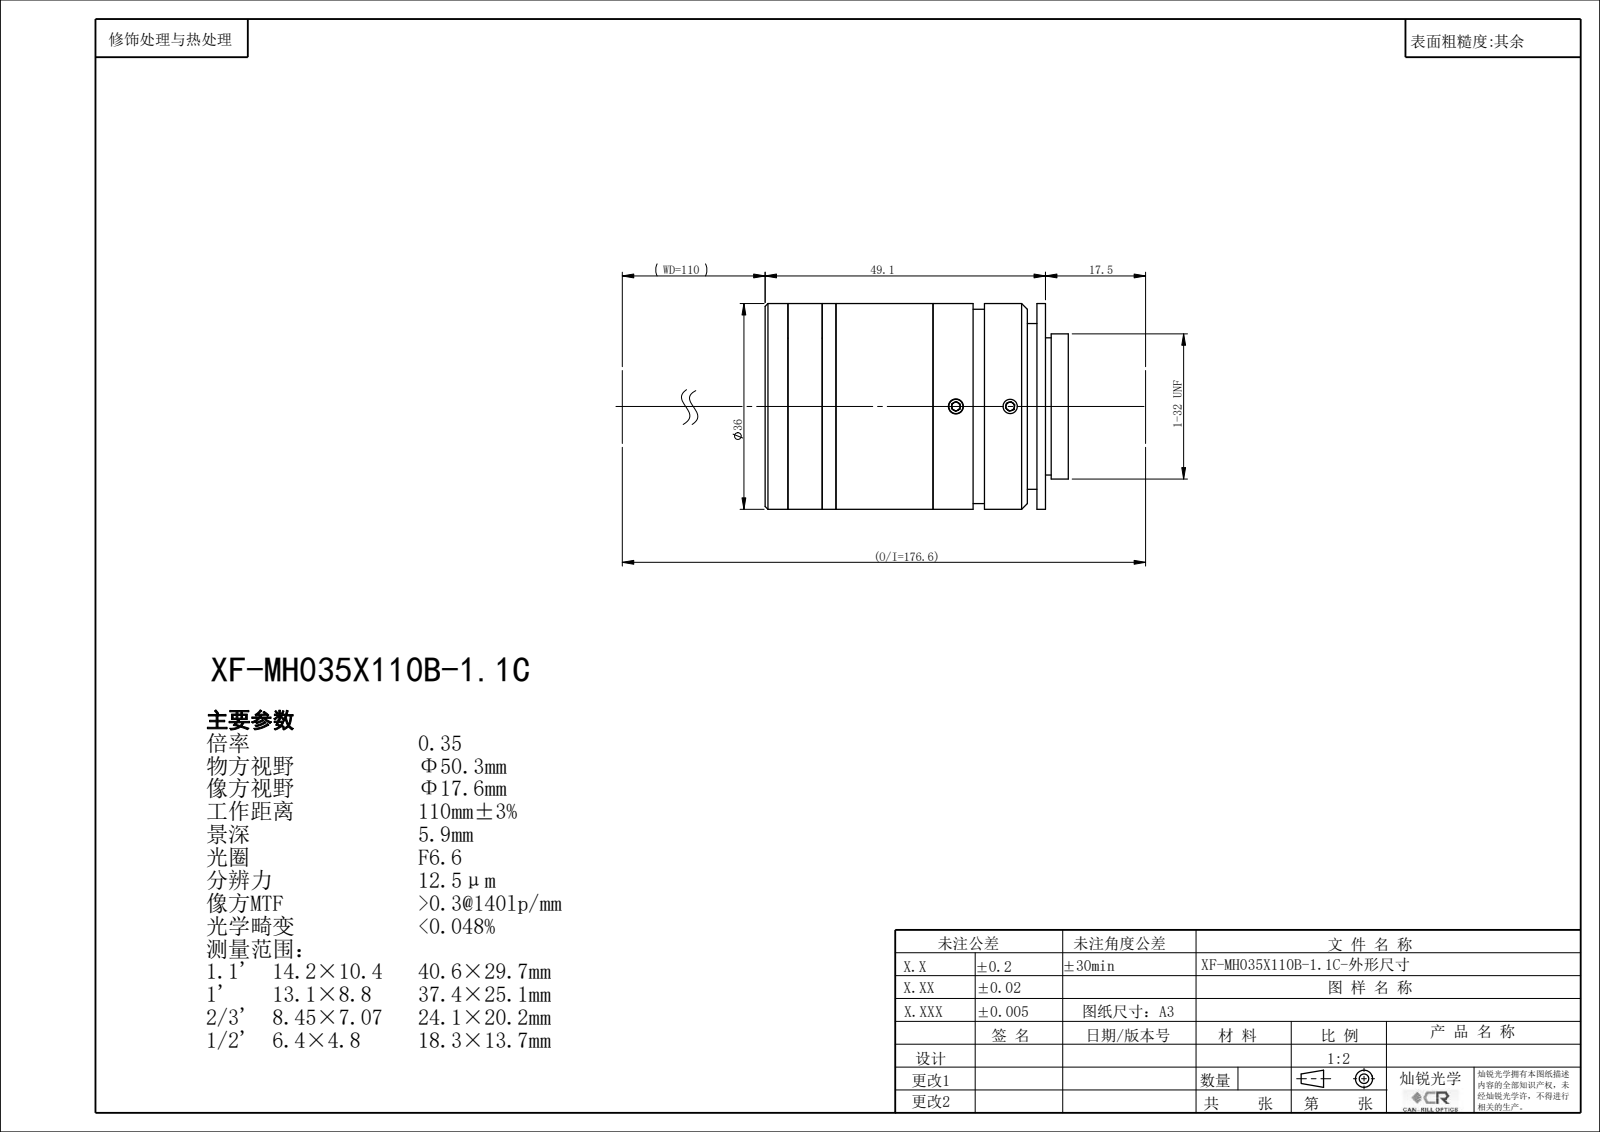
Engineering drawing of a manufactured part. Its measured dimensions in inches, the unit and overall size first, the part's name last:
Units: inches
Overall size (bounding box): 2.09 × 1.417 × 1.417
Round holes (diameter × count): ⌀0.098 ×3, ⌀0.551 ×1, ⌀0.646 ×1, ⌀0.669 ×1, ⌀0.724 ×1, ⌀0.882 ×1, ⌀0.945 ×1, ⌀0.98 ×1, ⌀1.024 ×1
Round bosses / shafts (diameter × count): ⌀1.417 ×1, ⌀1.339 ×1, ⌀1 ×1
Main face-to-face distances: 0.775, 1.932, 1.157, 0.059, 1.873, 0.716, 1.696, 0.488, 0.669, 1.385
Bodies: 0 solids, 156 faces (80 planar, 42 cylindrical, 34 other)
Part name (STEP PRODUCT): XF-MH035X110B-1.1C
STEP written by: SolidWorks 2022 (CONFIG_CONTROL_DESIGN)
